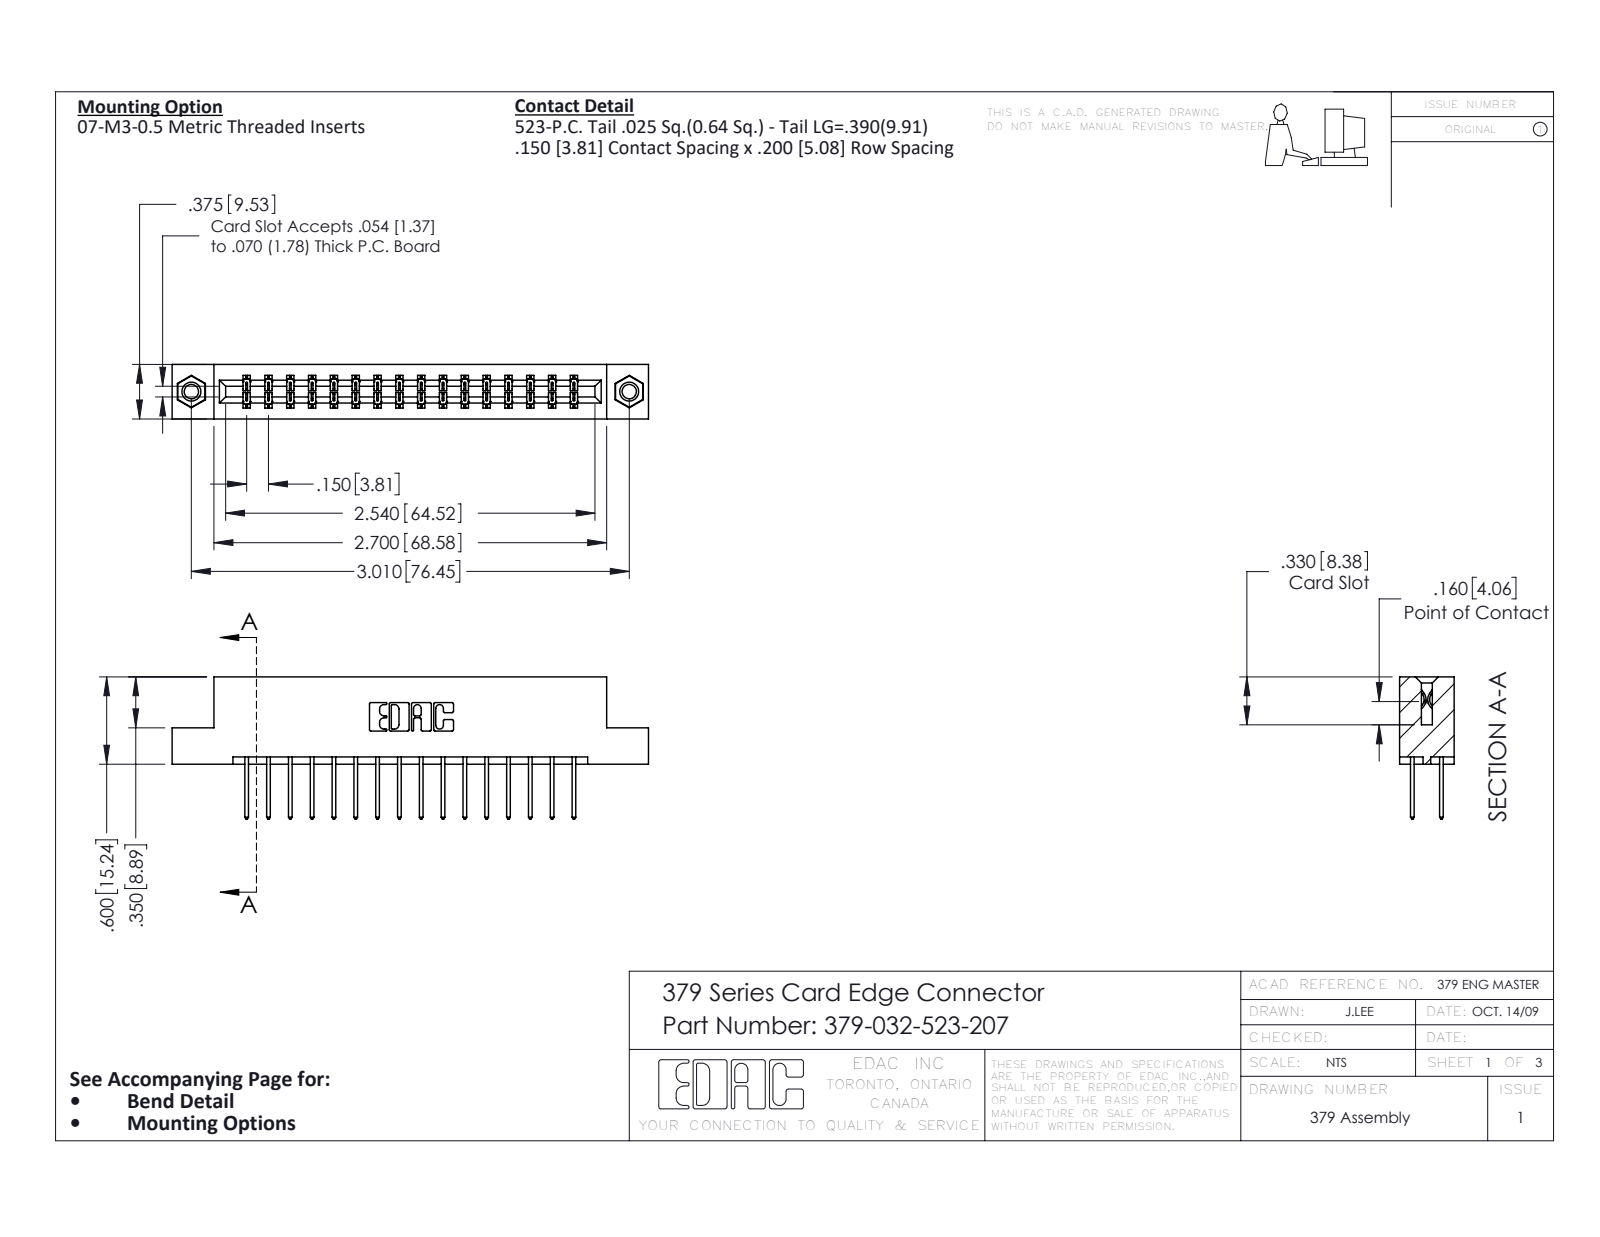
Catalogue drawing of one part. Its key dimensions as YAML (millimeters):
part_name: "345-292-001_345-293-123; 379 Part_Flush - .156 Dia - TI; 345-250-001_345-250-005-103; 379-032-523-207"
step_written_by: "SolidWorks 2020 (CONFIG_CONTROL_DESIGN)"
units: millimeters
bodies: {solids: 35, faces: 1838, planar: 1254, cylindrical: 568, other: 16}
overall_size: [83.2, 24.8, 9.5]
volume: 8590
surface_area: 9755
round_holes:
  - {diameter: 2.5, count: 2}
  - {diameter: 3.2, count: 2}
  - {diameter: 4, count: 2}
round_bosses_or_shafts:
  - {diameter: 3.9, count: 2}
partial_cylinders:
  - {radius: 0.2, count: 63}
  - {radius: 0.3, count: 32}
  - {radius: 0.3, count: 22}
  - {radius: 0.2, count: 6}
  - {radius: 0.8, count: 6}
  - {radius: 0.7, count: 3}
  - {radius: 0.4, count: 2}
  - {radius: 0.6, count: 2}
face_to_face_distances: [7.6, 1.9, 5.1, 9.5, 2.5, 3.8, 1.3, 15.2, 5.7, 7]
hole_center_spacings: [76.5]
